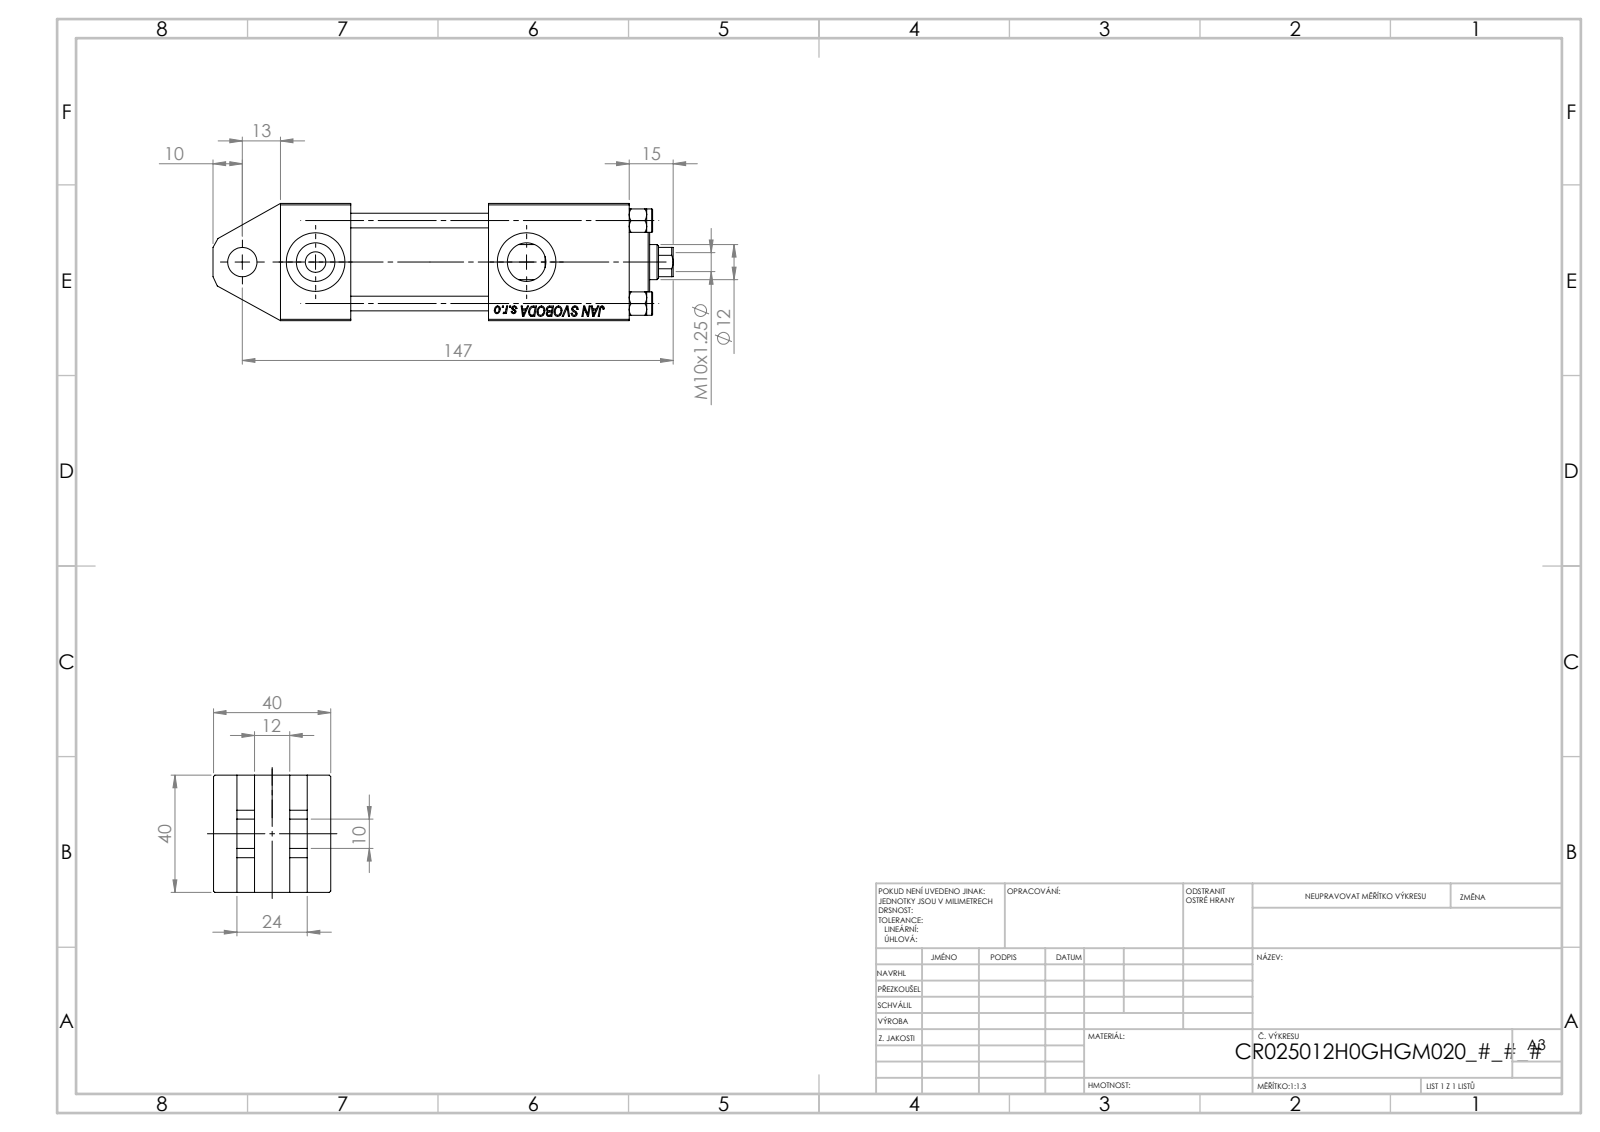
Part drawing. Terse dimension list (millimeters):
name: V215CR_H_Body; NUT_M5_H; V215CR_VCP_H; V215_VC_A (+1 more)
written by: SolidWorks 2019 (CONFIG_CONTROL_DESIGN)
unit: mm
bodies: 11 solids, 1136 faces (517 planar, 87 cylindrical, 532 other)
size: 157 × 40 × 40
volume: 149 773 mm³; area: 59 607 mm²
holes: 4× ⌀5, 3× ⌀20, 2× ⌀2.5, 2× ⌀7, 2× ⌀13.16, 1× ⌀6.5, 1× ⌀10, 1× ⌀12, 1× ⌀15, 1× ⌀25, 1× ⌀30
bosses: 4× ⌀8, 1× ⌀31, 1× ⌀24
rounds: 1× R5.5
face distances: 40, 24, 8, 32, 6, 14, 26, 18, 47, 90.3
hole spacings: 14.18, 20.01, 28.3, 30.84, 13.25, 40.02, 25, 26.5
